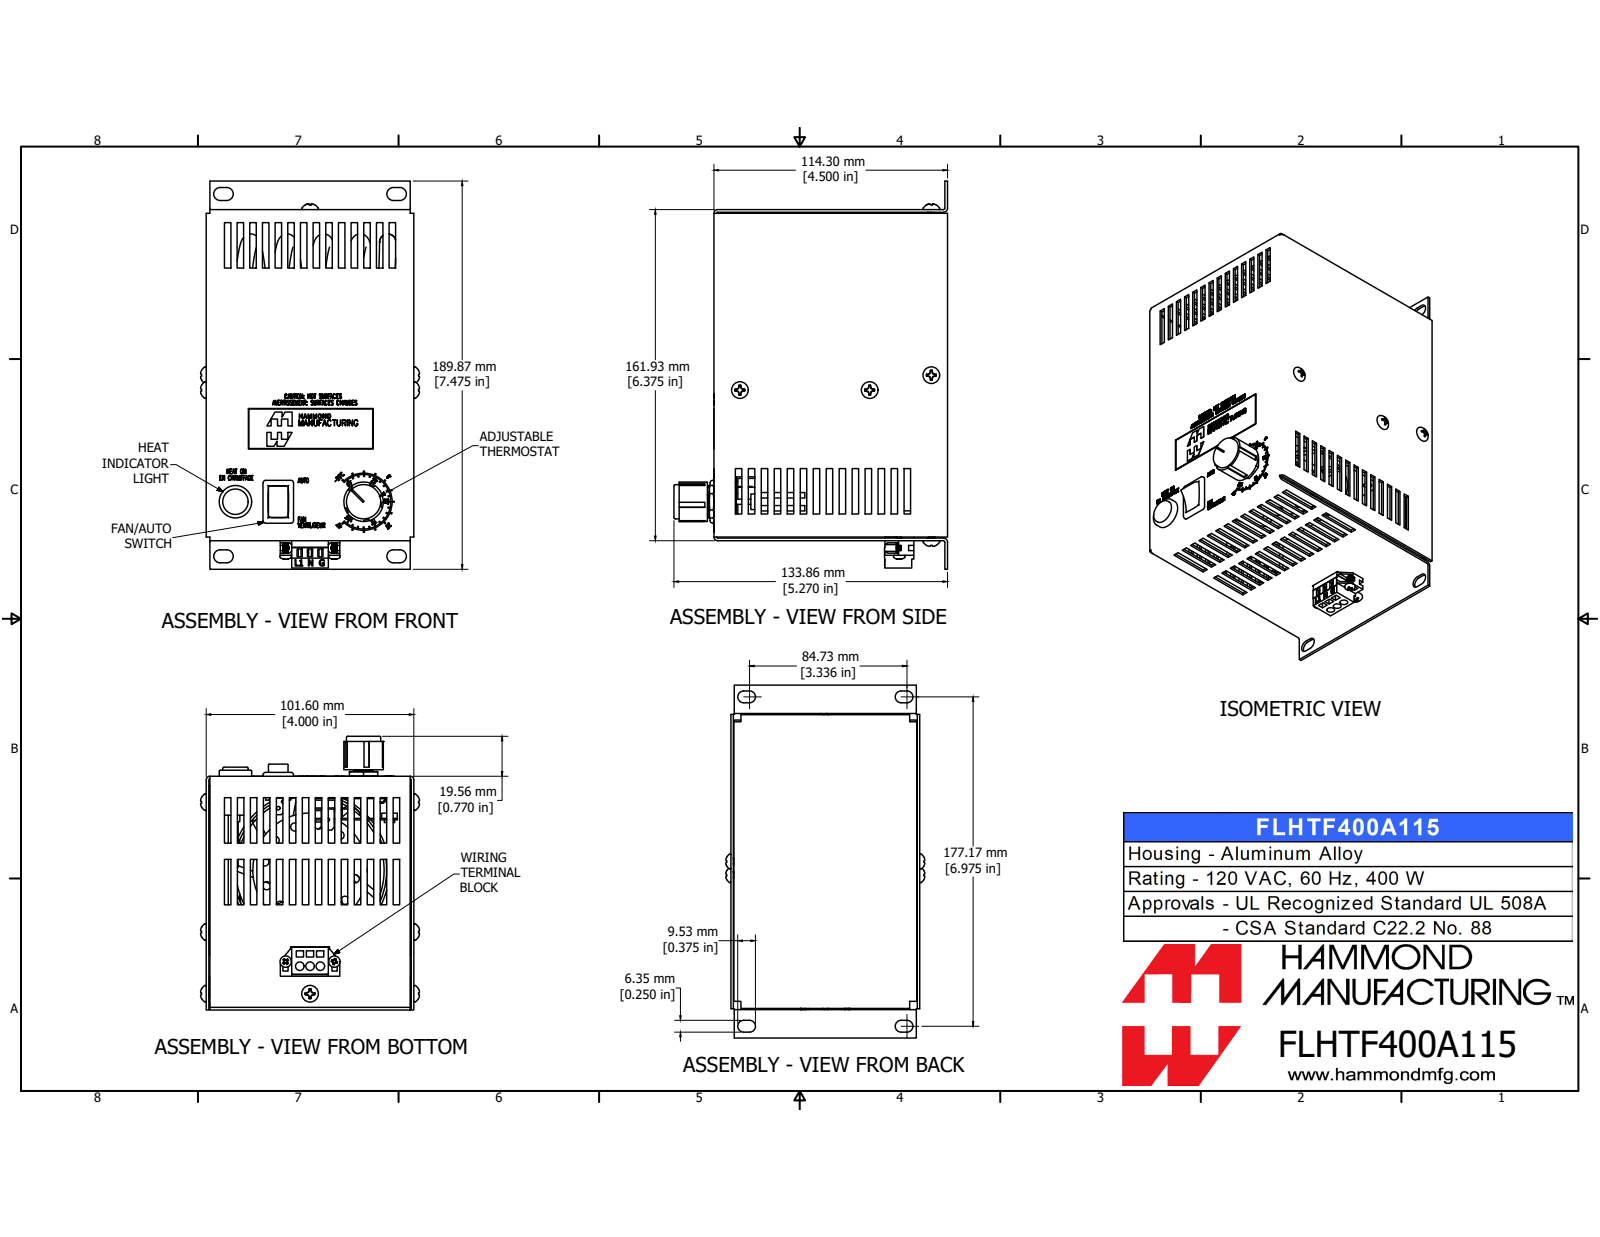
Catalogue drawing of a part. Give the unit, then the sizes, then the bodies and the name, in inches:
Units: inches
Overall size (bounding box): 7.475 × 5.27 × 4.218
Round holes (diameter × count): ⌀0.137 ×4, ⌀0.182 ×4, ⌀0.203 ×4, ⌀0.165 ×3, ⌀0.085 ×2, ⌀0.12 ×2, ⌀0.13 ×2, ⌀0.189 ×2, ⌀0.066 ×1, ⌀0.07 ×1, ⌀0.25 ×1, ⌀0.383 ×1
Round bosses / shafts (diameter × count): ⌀0.164 ×4, ⌀0.104 ×4, ⌀0.17 ×2, ⌀0.105 ×2, ⌀0.76 ×1, ⌀0.66 ×1, ⌀0.65 ×1, ⌀0.625 ×1
Partial cylindrical surfaces — rounded edges, fillets, slot ends (radius × count): R0.125 ×38, R0.05 ×17, R0.629 ×12, R0.15 ×9, R0.025 ×8, R0.02 ×4, R0.071 ×4, R0.015 ×2
Main face-to-face distances: 0.051, 3.949, 0.1, 0.051, 6.324, 4, 3.898, 4.442, 4.493, 4.342
Hole centre spacings: 2.756, 0.197, 0.286, 0.477, 0.564, 0.565, 0.672, 0.776
Volume: 11.03 in³ · Surface area: 345 in²
Bodies: 17 solids, 4227 faces (3719 planar, 274 cylindrical, 234 other)
Part name (STEP PRODUCT): FLHTF400A115
STEP written by: SolidWorks 2019 (AUTOMOTIVE_DESIGN)
